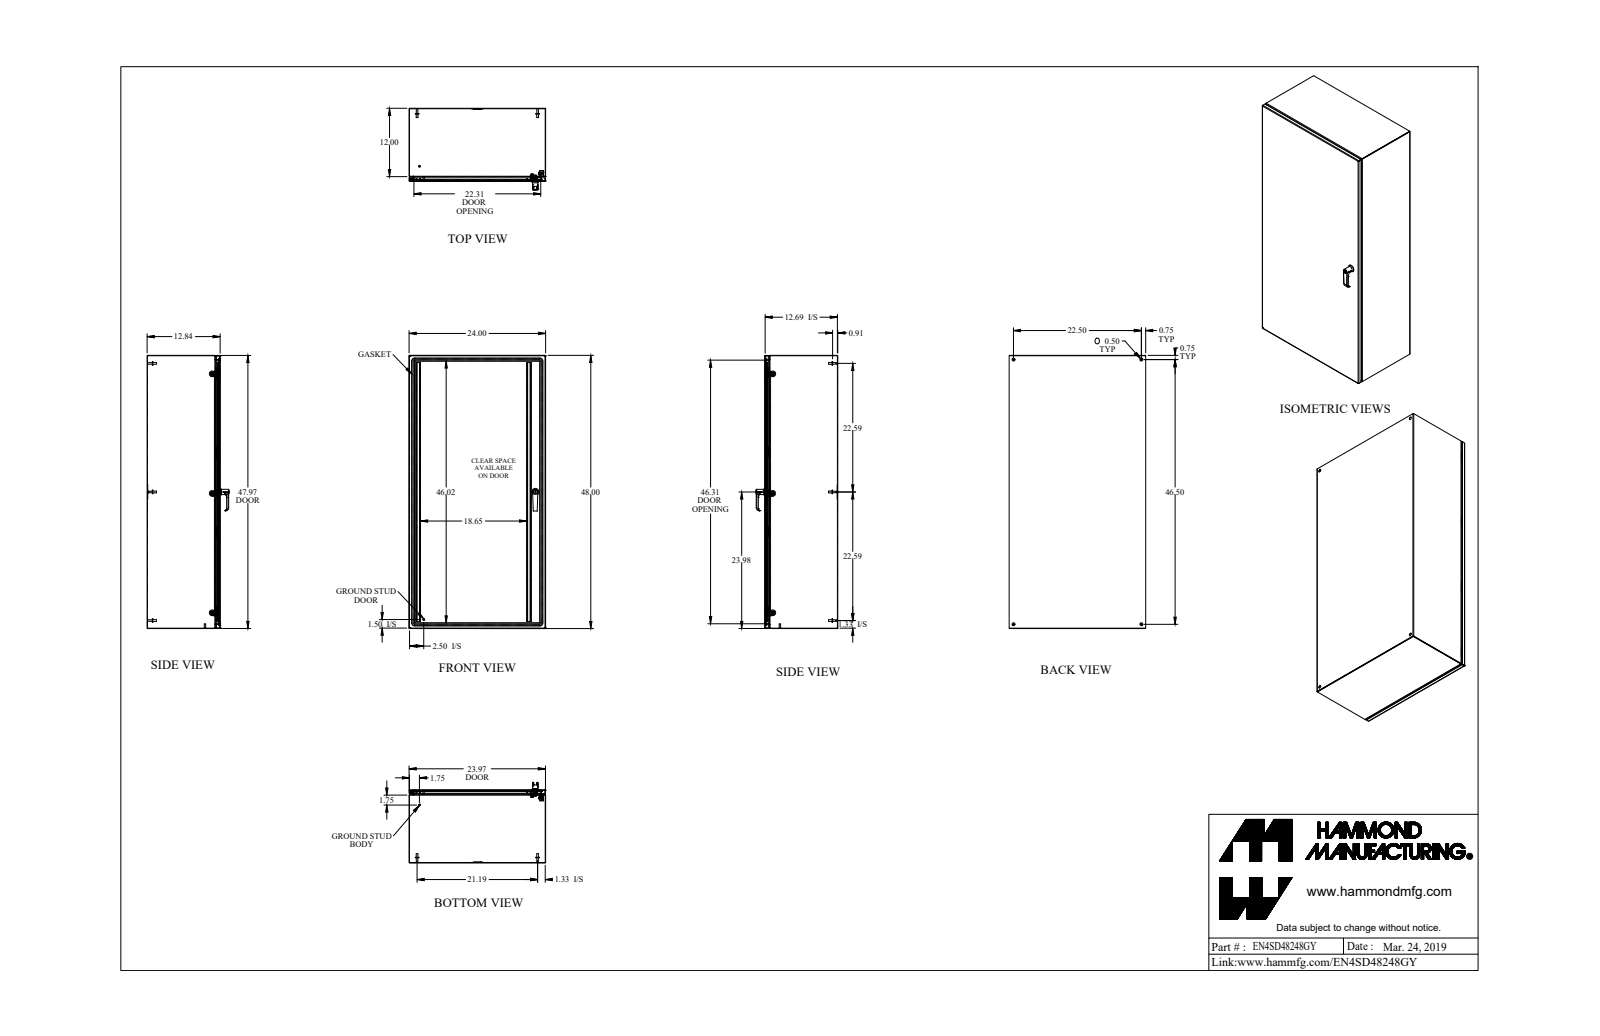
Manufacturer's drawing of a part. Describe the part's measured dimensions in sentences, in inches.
The part is named "EN4SD48248GY_Default". Its 3-D file was written by "SolidWorks 2019 (CONFIG_CONTROL_DESIGN)". It is 53 solids with 1457 faces: 632 planar, 538 cylindrical and 287 other. Overall it measures 48 by 24 by 10.367 inches. Its volume is 298.8 cubic inches and its surface area 8 294 square inches. Round holes: 6 of diameter 0.176, 4 of diameter 0.5, 3 of diameter 0.196, 3 of diameter 0.25, 3 of diameter 0.265, 3 of diameter 0.413, 2 of diameter 0.256, 2 of diameter 0.313, 2 of diameter 0.394, 1 of diameter 0.172, 1 of diameter 0.24, 1 of diameter 0.242. Round bosses or shafts: 7 of diameter 0.25, 6 of diameter 0.625, 6 of diameter 0.313, 6 of diameter 0.27, 6 of diameter 0.156, 5 of diameter 0.375, 3 of diameter 1, 2 of diameter 0.63. Partial cylindrical surfaces (rounded edges, fillets, slot ends): 20 of radius 0.036, 20 of radius 0.108, 15 of radius 0.03, 12 of radius 0.043, 12 of radius 0.081, 8 of radius 0.006, 8 of radius 0.04, 8 of radius 0.062. The main face-to-face distances are 0.072, 8.765, 8.693, 8.837, 23.928, 23.856, 24, 47.928, 47.856, 48. The hole center spacings are 0.787, 20.982, 21, 21.547, 22.5, 41.969, 46.5, 51.657.
